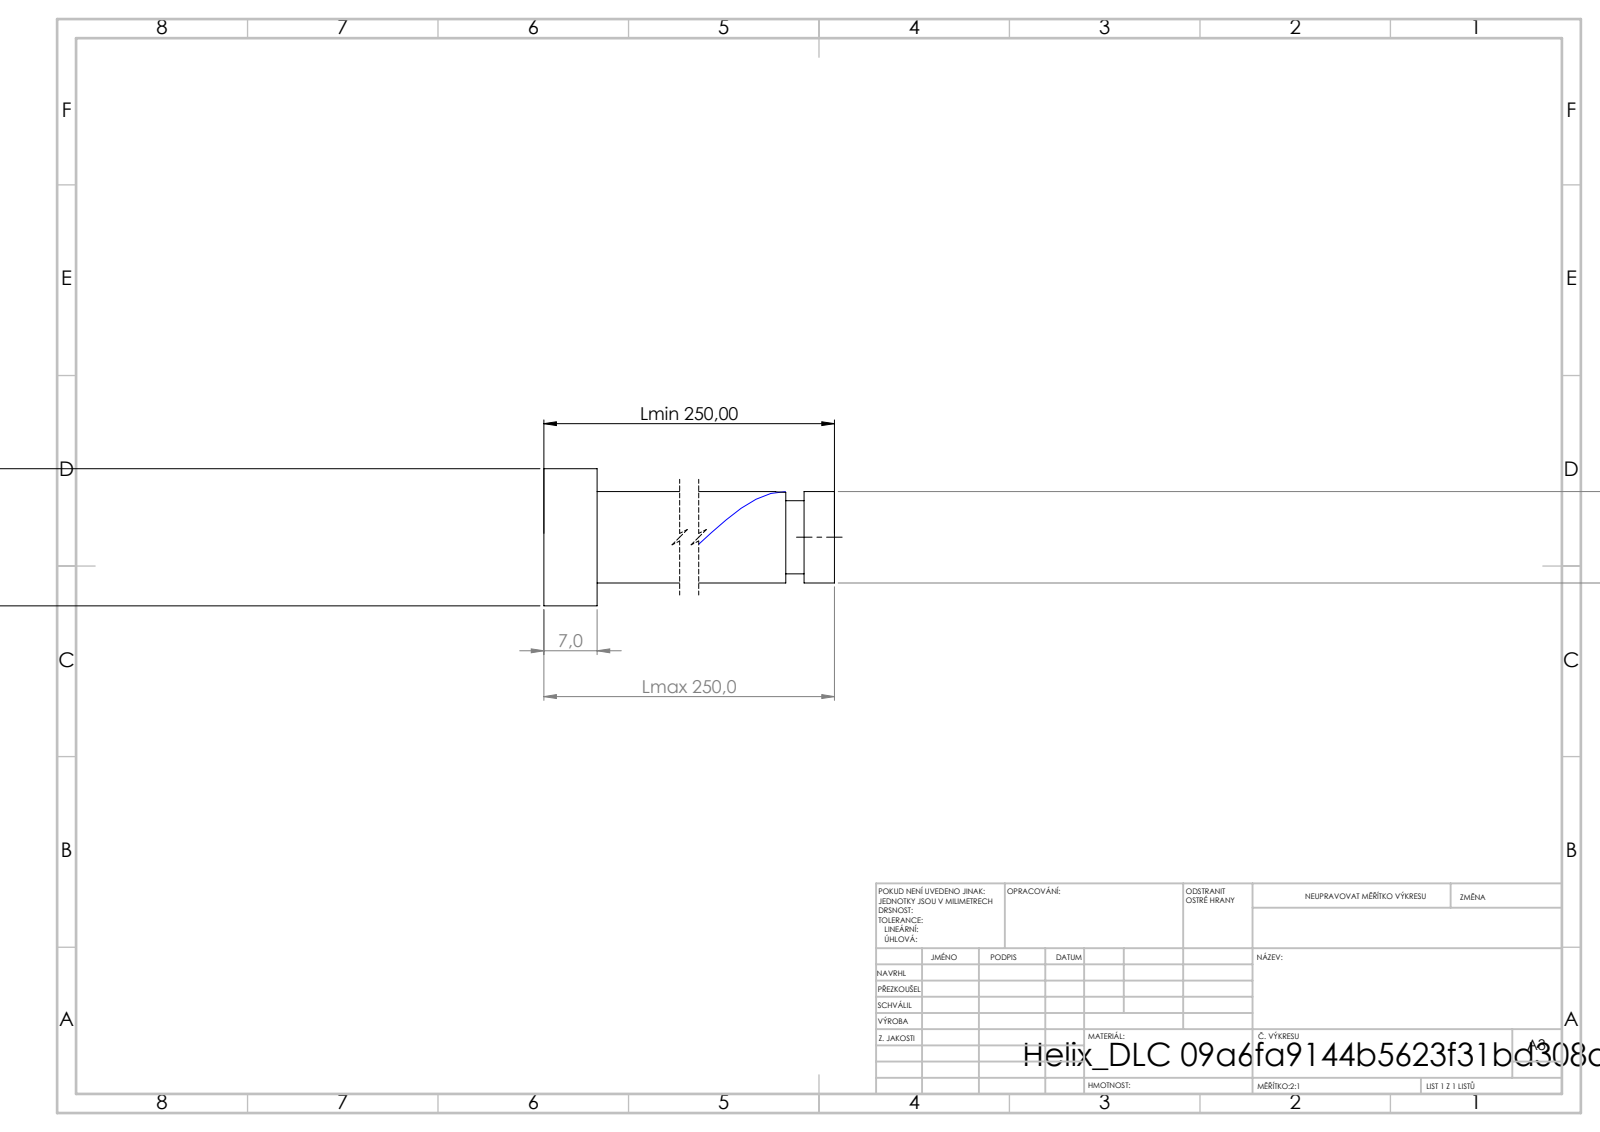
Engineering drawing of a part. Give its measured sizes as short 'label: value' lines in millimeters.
written by: SolidWorks 2019 (CONFIG_CONTROL_DESIGN)
unit: mm
bodies: 1 solid, 21 faces (6 planar, 14 cylindrical, 1 other)
size: 250 × 18 × 18
volume: 28 896 mm³; area: 10 344 mm²
bosses: 1× ⌀18, 1× ⌀12, 1× ⌀9.6
face distances: 7, 250, 243, 246.01, 239.01, 3.99, 243.61, 236.61, 2.4, 6.39
